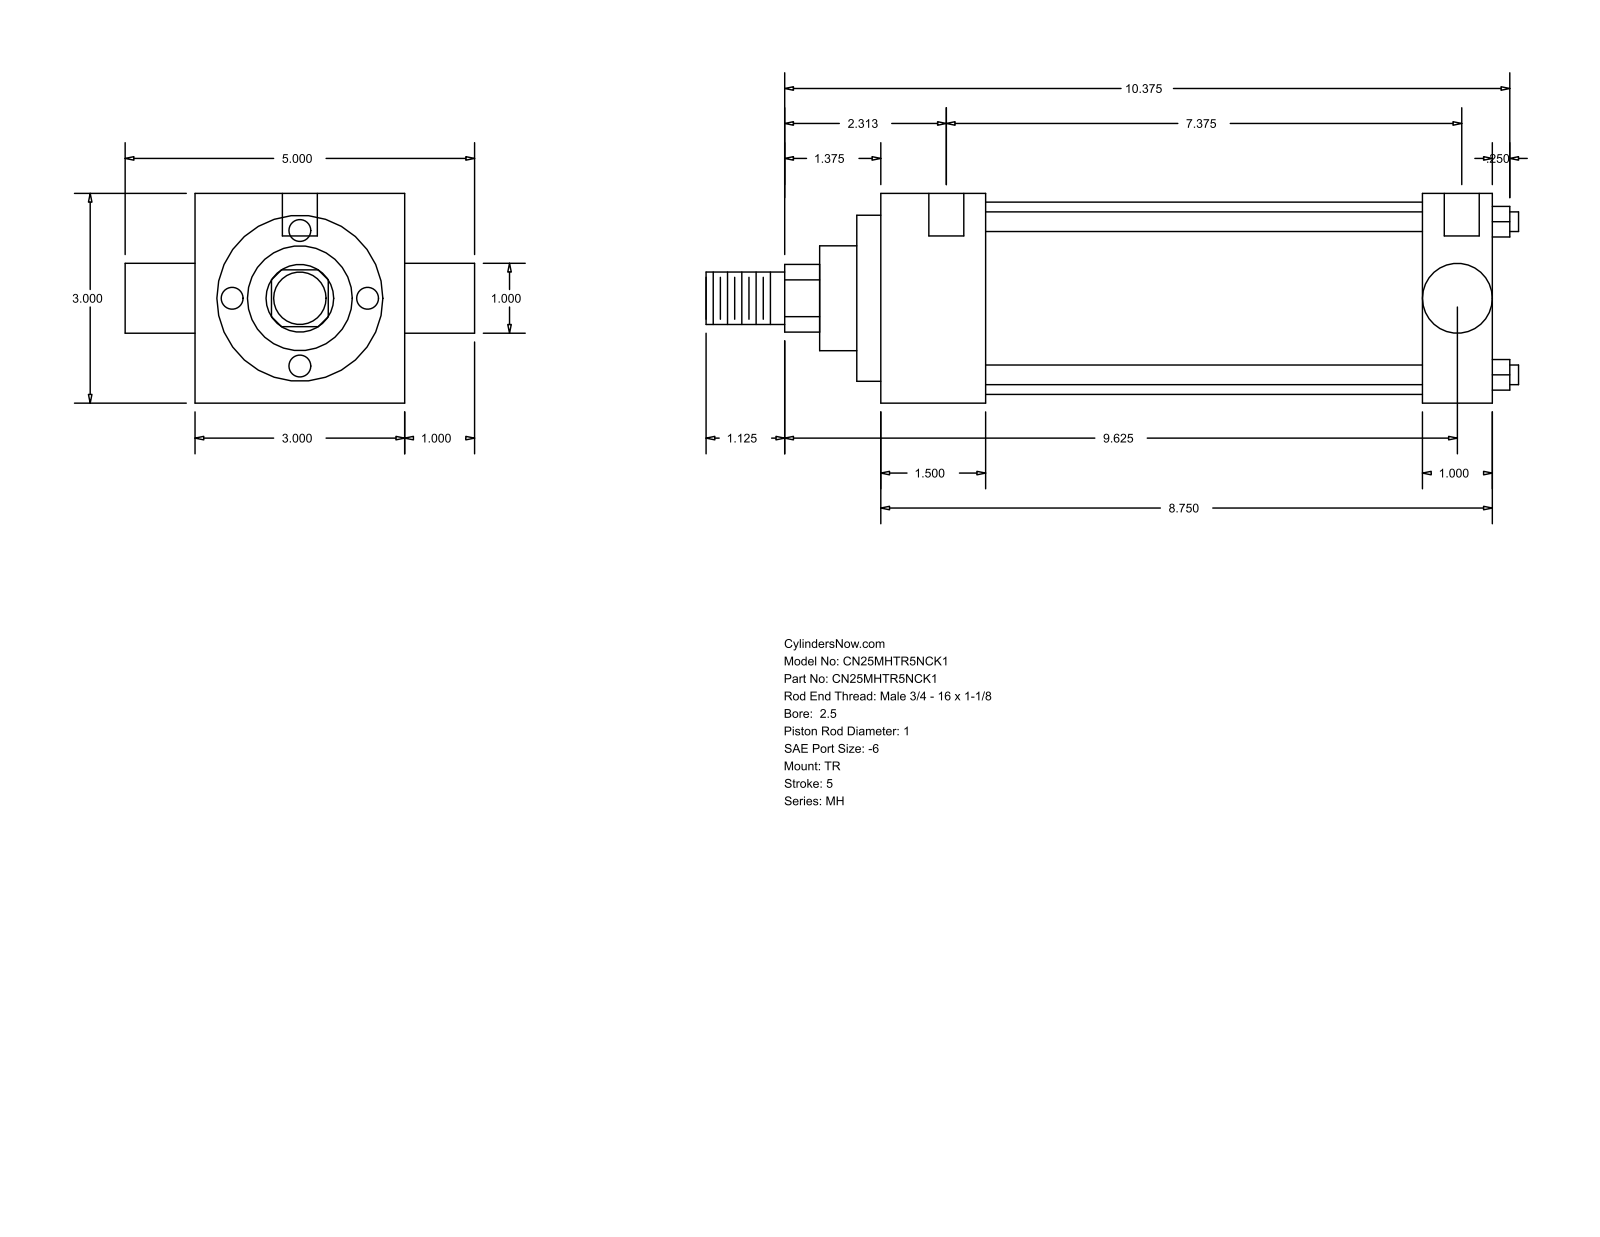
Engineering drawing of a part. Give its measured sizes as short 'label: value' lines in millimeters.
name: MH_TR__0250_1
written by: GSSL Pune (CONFIG_CONTROL_DESIGN)
unit: mm
bodies: 0 solids, 86 faces (61 planar, 25 cylindrical, 0 other)
size: 295.27 × 127 × 76.2
holes: 3× ⌀5.56, 2× ⌀12.7
bosses: 4× ⌀7.14, 1× ⌀69.85, 1× ⌀60.33, 1× ⌀38.1, 1× ⌀25.4, 1× ⌀25.35, 1× ⌀19.05
rounds: 1× R12.29
face distances: 76.2, 222.26, 25.4, 38.11, 184.15, 196.86, 158.75, 8.73, 46.84, 205.59
hole spacings: 3.18, 4.76, 187.32, 190.5, 192.08, 195.26
